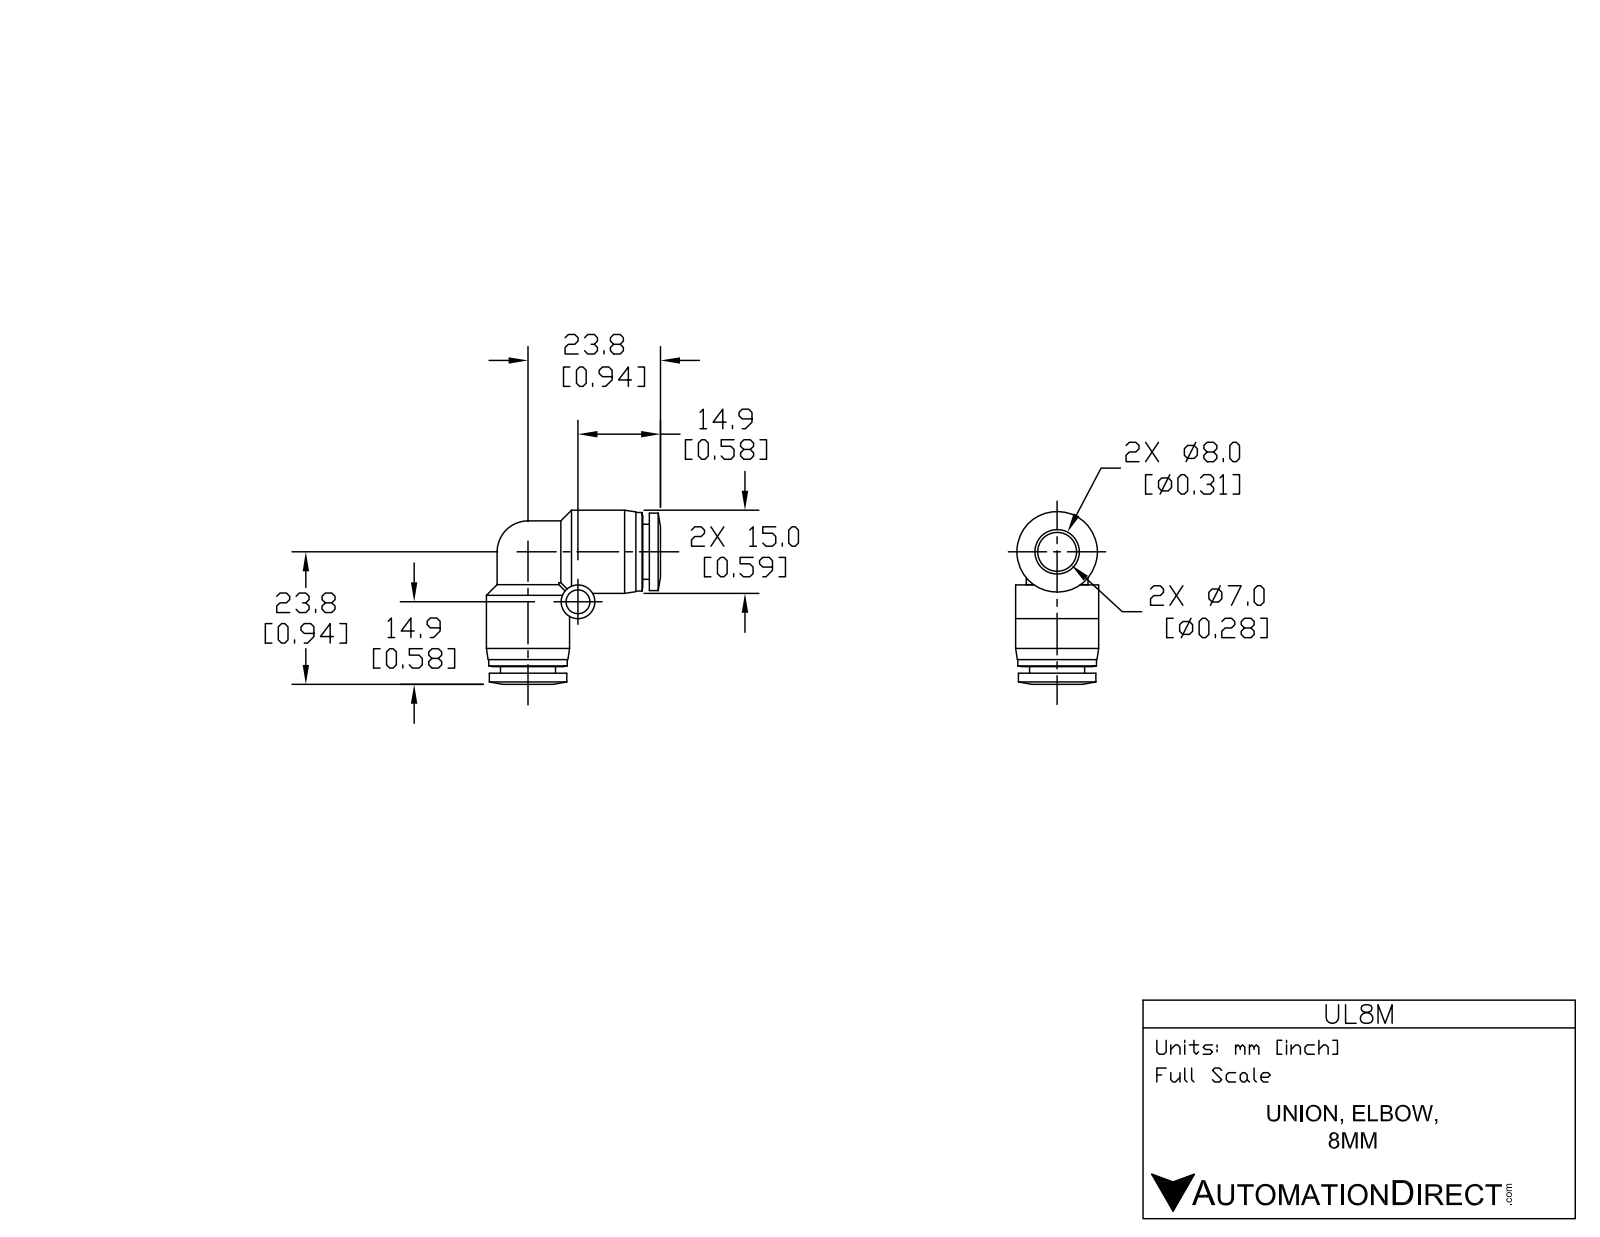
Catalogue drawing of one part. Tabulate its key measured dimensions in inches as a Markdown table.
| quantity | value |
| --- | --- |
| part name | UL8M |
| STEP written by | SolidWorks 2015 (AUTOMOTIVE_DESIGN) |
| units | inches |
| bodies | 1 solid, 68 faces (12 planar, 32 cylindrical, 24 other) |
| overall size | 1.22 × 1.22 × 0.583 |
| volume | 0.268 in³ |
| surface area | 6.244 in² |
| round holes (diameter × count) | 0.268 × 2, 0.327 × 2, 0.165 × 1 |
| round bosses / shafts (diameter × count) | 0.583 × 2, 0.551 × 2, 0.543 × 2, 0.433 × 2, 0.386 × 2, 0.236 × 1 |
| main face-to-face distances | 0.045, 0.596, 0.642, 0.583, 0.72, 0.124, 0.079, 0.547, 0.049, 0.094 |
